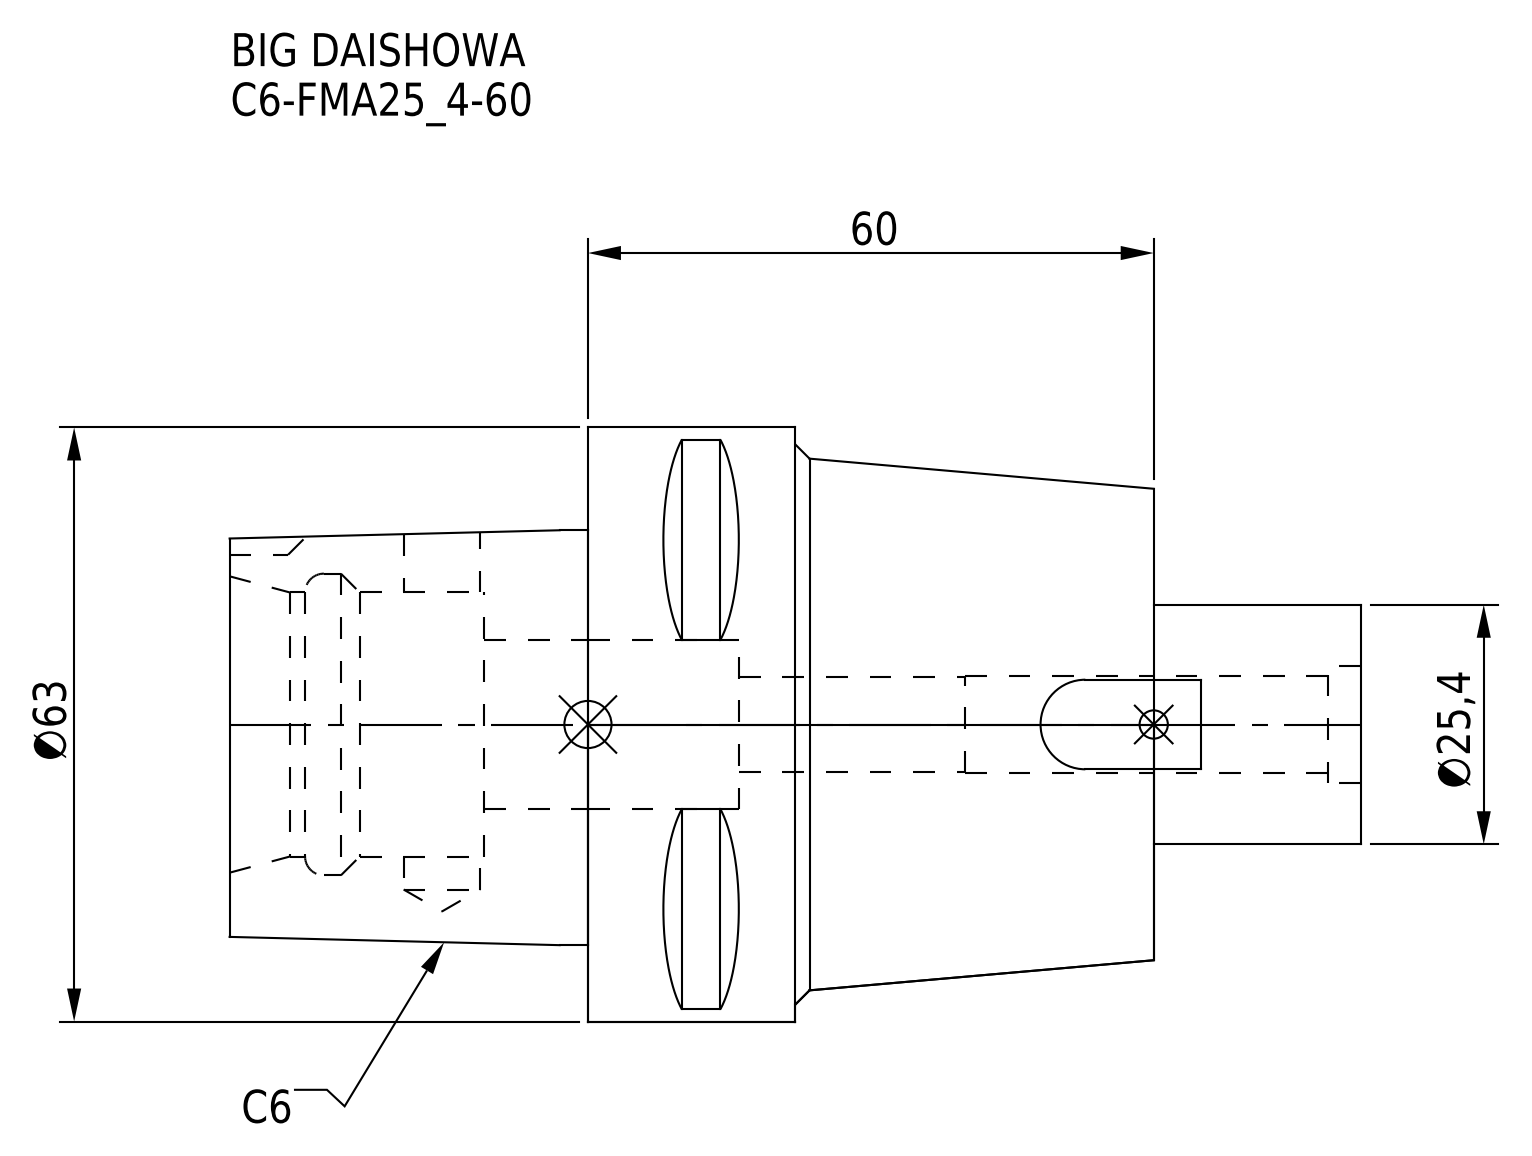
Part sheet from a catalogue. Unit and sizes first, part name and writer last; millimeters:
Units: millimetres
Overall size (bounding box): 120 × 63 × 63
Round holes (diameter × count): ⌀8.1 ×1, ⌀10 ×1, ⌀10.25 ×1, ⌀12.5 ×1, ⌀18 ×1, ⌀28 ×1, ⌀32 ×1
Round bosses / shafts (diameter × count): ⌀63 ×1, ⌀25.4 ×1
Partial cylindrical surfaces — rounded edges, fillets, slot ends (radius × count): R5 ×1
Main face-to-face distances: 60, 38, 22, 27, 98, 11, 82, 120, 93, 71
Volume: 188 447 mm³ · Surface area: 29 991 mm²
Bodies: 1 solid, 78 faces (41 planar, 23 cylindrical, 14 other)
Part name (STEP PRODUCT): C6-FMA25_4-60
STEP written by: CREO PARAMETRIC BY PTC INC, 2016380 (AUTOMOTIVE_DESIGN)
